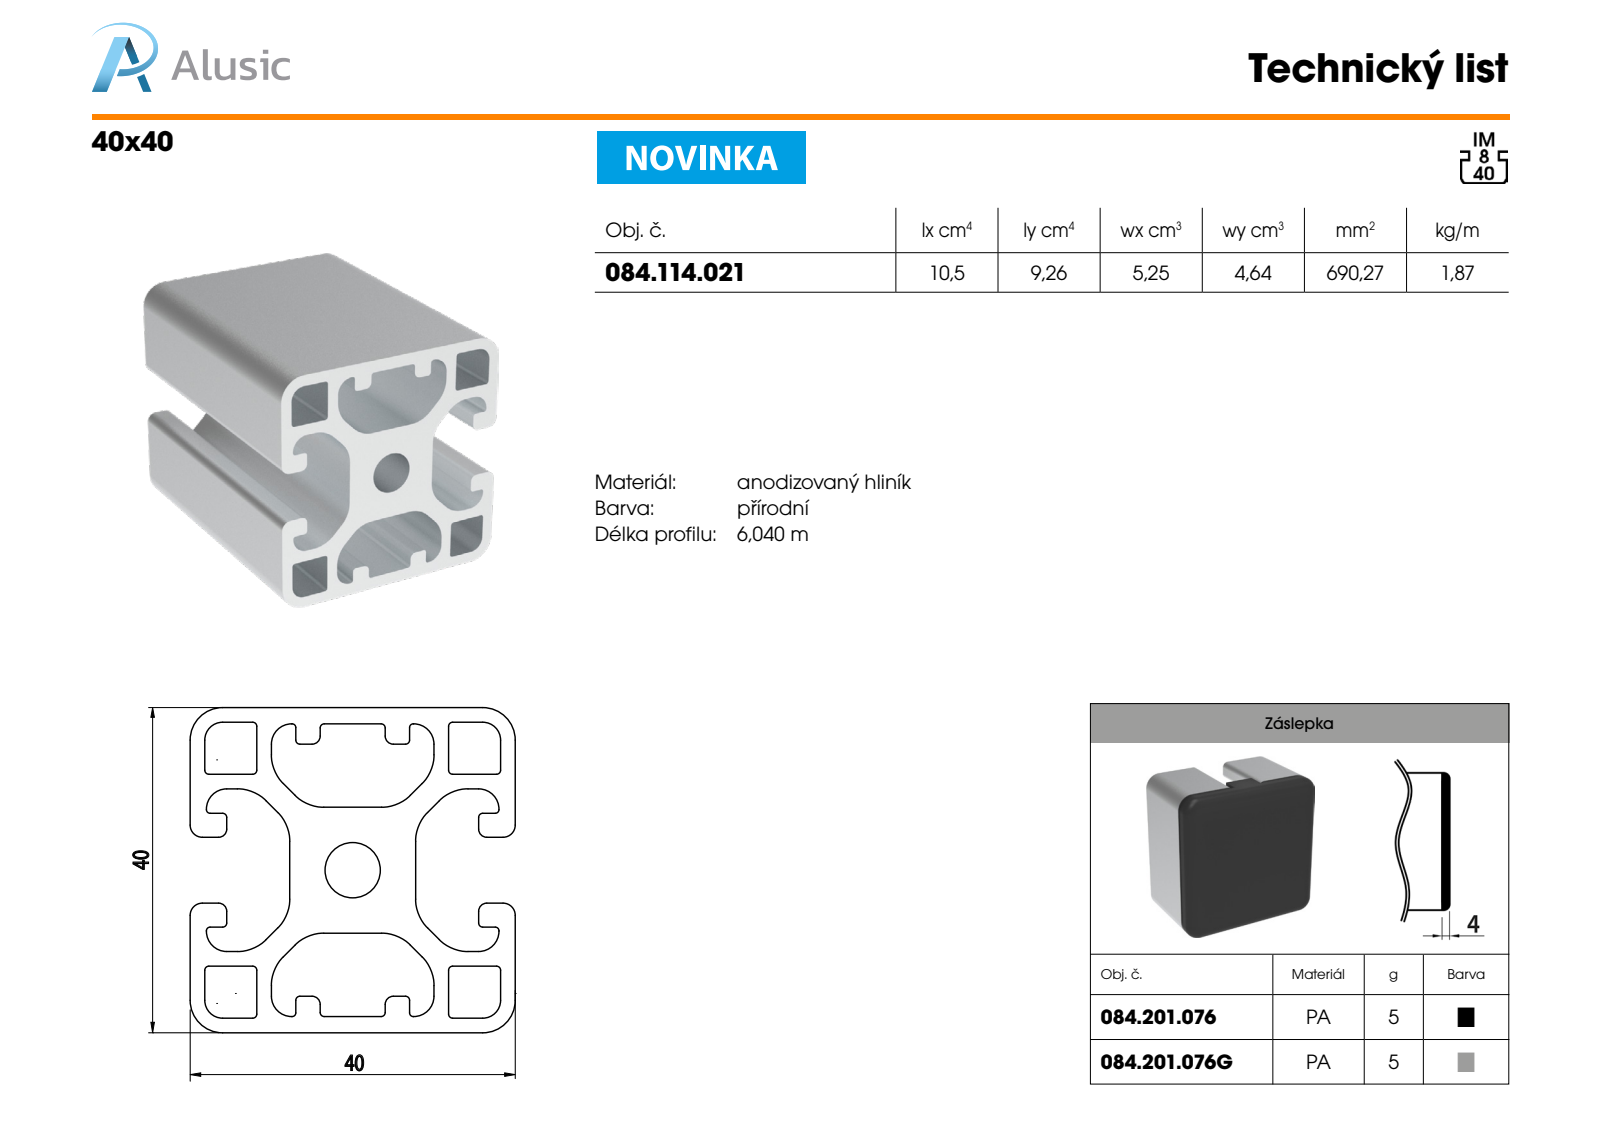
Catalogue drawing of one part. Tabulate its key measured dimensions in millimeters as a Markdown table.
| quantity | value |
| --- | --- |
| part name | 084.114.021 |
| STEP written by | SolidWorks 2018 (AUTOMOTIVE_DESIGN) |
| units | millimeters |
| bodies | 1 solid, 156 faces (78 planar, 78 cylindrical, 0 other) |
| overall size | 100 × 40 × 40 |
| volume | 69 028 mm³ |
| surface area | 49 930 mm² |
| round holes (diameter × count) | 6.8 × 1 |
| partial cylindrical surfaces (radius × count) | 0.5 × 24, 5 × 16, 0.45 × 8, 1 × 8, 2.5 × 8, 1.5 × 4, 2.2 × 4, 4 × 4 |
| main face-to-face distances | 8.2, 40, 31.8, 30, 1.8, 19.55, 38.2, 6.4, 12.25, 27.75 |
